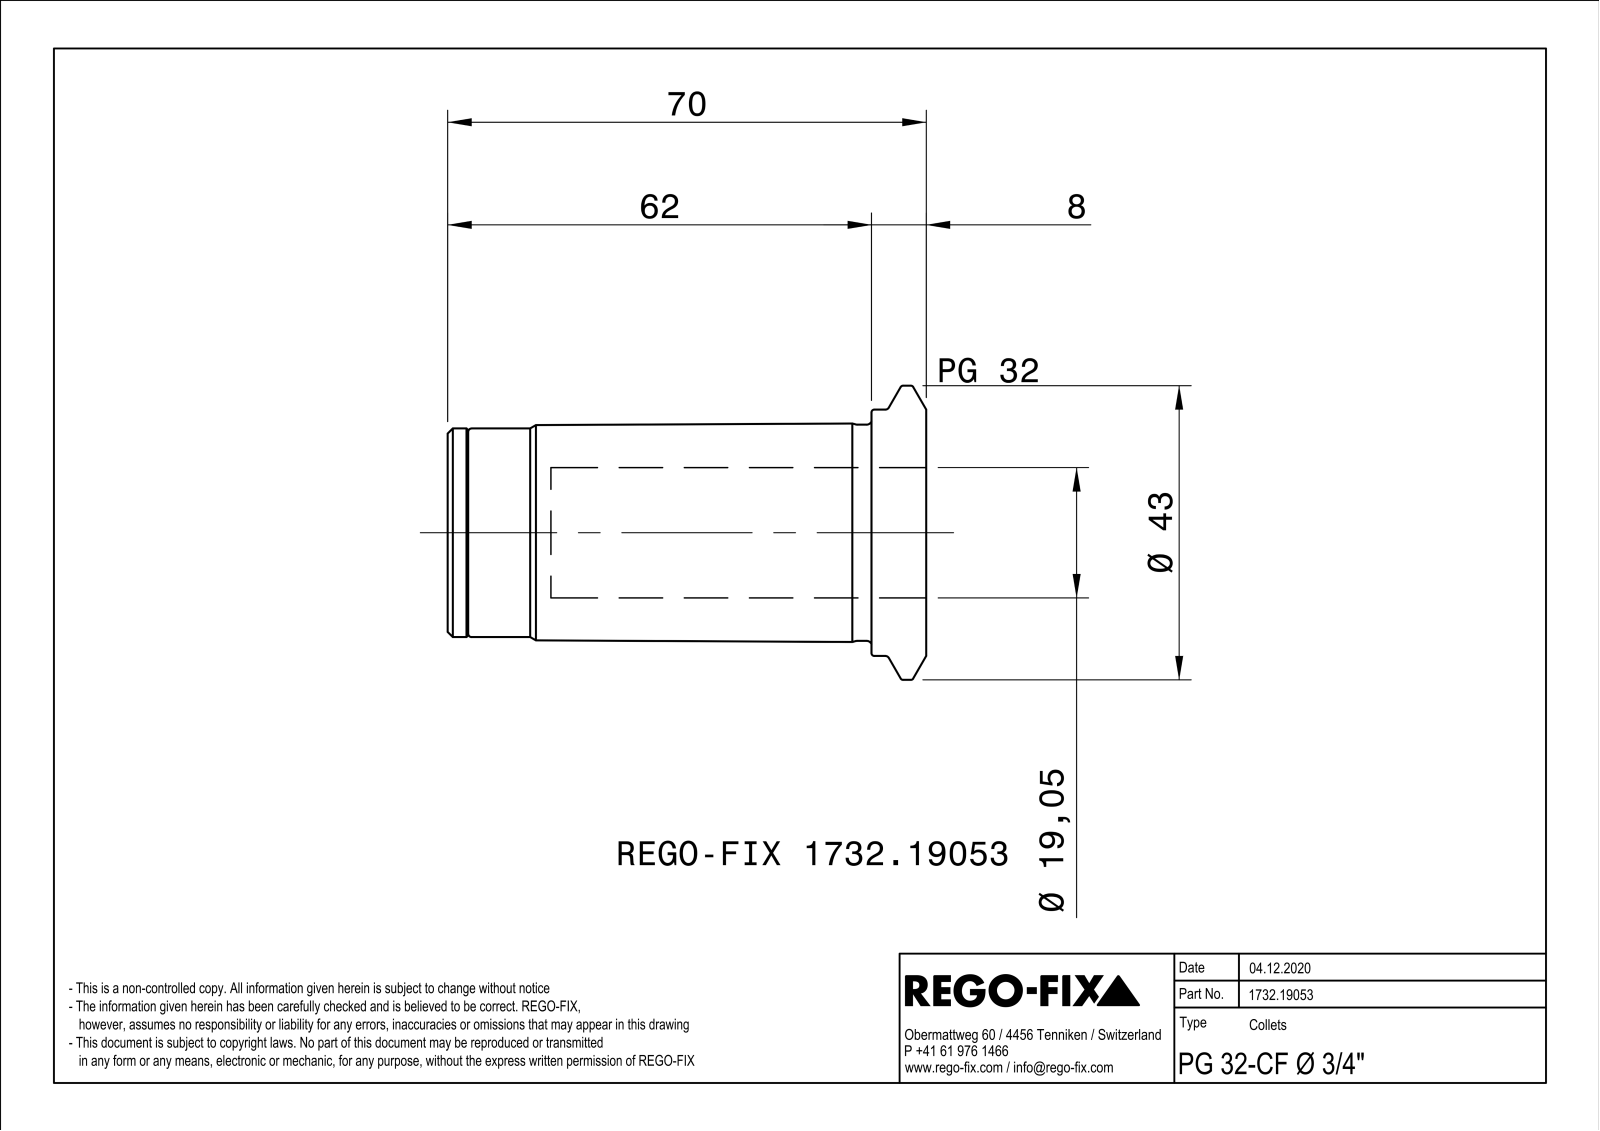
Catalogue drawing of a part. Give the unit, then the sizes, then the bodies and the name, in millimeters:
Units: millimetres
Overall size (bounding box): 70 × 43 × 42.99
Round holes (diameter × count): ⌀4 ×3, ⌀8.92 ×1, ⌀10.5 ×1, ⌀19.05 ×1, ⌀26.92 ×1, ⌀28.5 ×1
Round bosses / shafts (diameter × count): ⌀43 ×1, ⌀36 ×1, ⌀31.6 ×1, ⌀30.5 ×1, ⌀26.5 ×1, ⌀21 ×1
Partial cylindrical surfaces — rounded edges, fillets, slot ends (radius × count): R2 ×6, R1 ×3, R3.5 ×3, R3.98 ×1, R4.75 ×1, R8.75 ×1
Main face-to-face distances: 1, 70, 58, 12, 59, 11, 8, 60, 2, 10
Hole centre spacings: 7.75, 13.42, 13.43
Volume: 37 274 mm³ · Surface area: 16 750 mm²
Bodies: 1 solid, 130 faces (31 planar, 45 cylindrical, 54 other)
Part name (STEP PRODUCT): NOCUT
STEP written by: SIEMENS PLM Software Solid Edge ST10 (AUTOMOTIVE_DESIGN)
